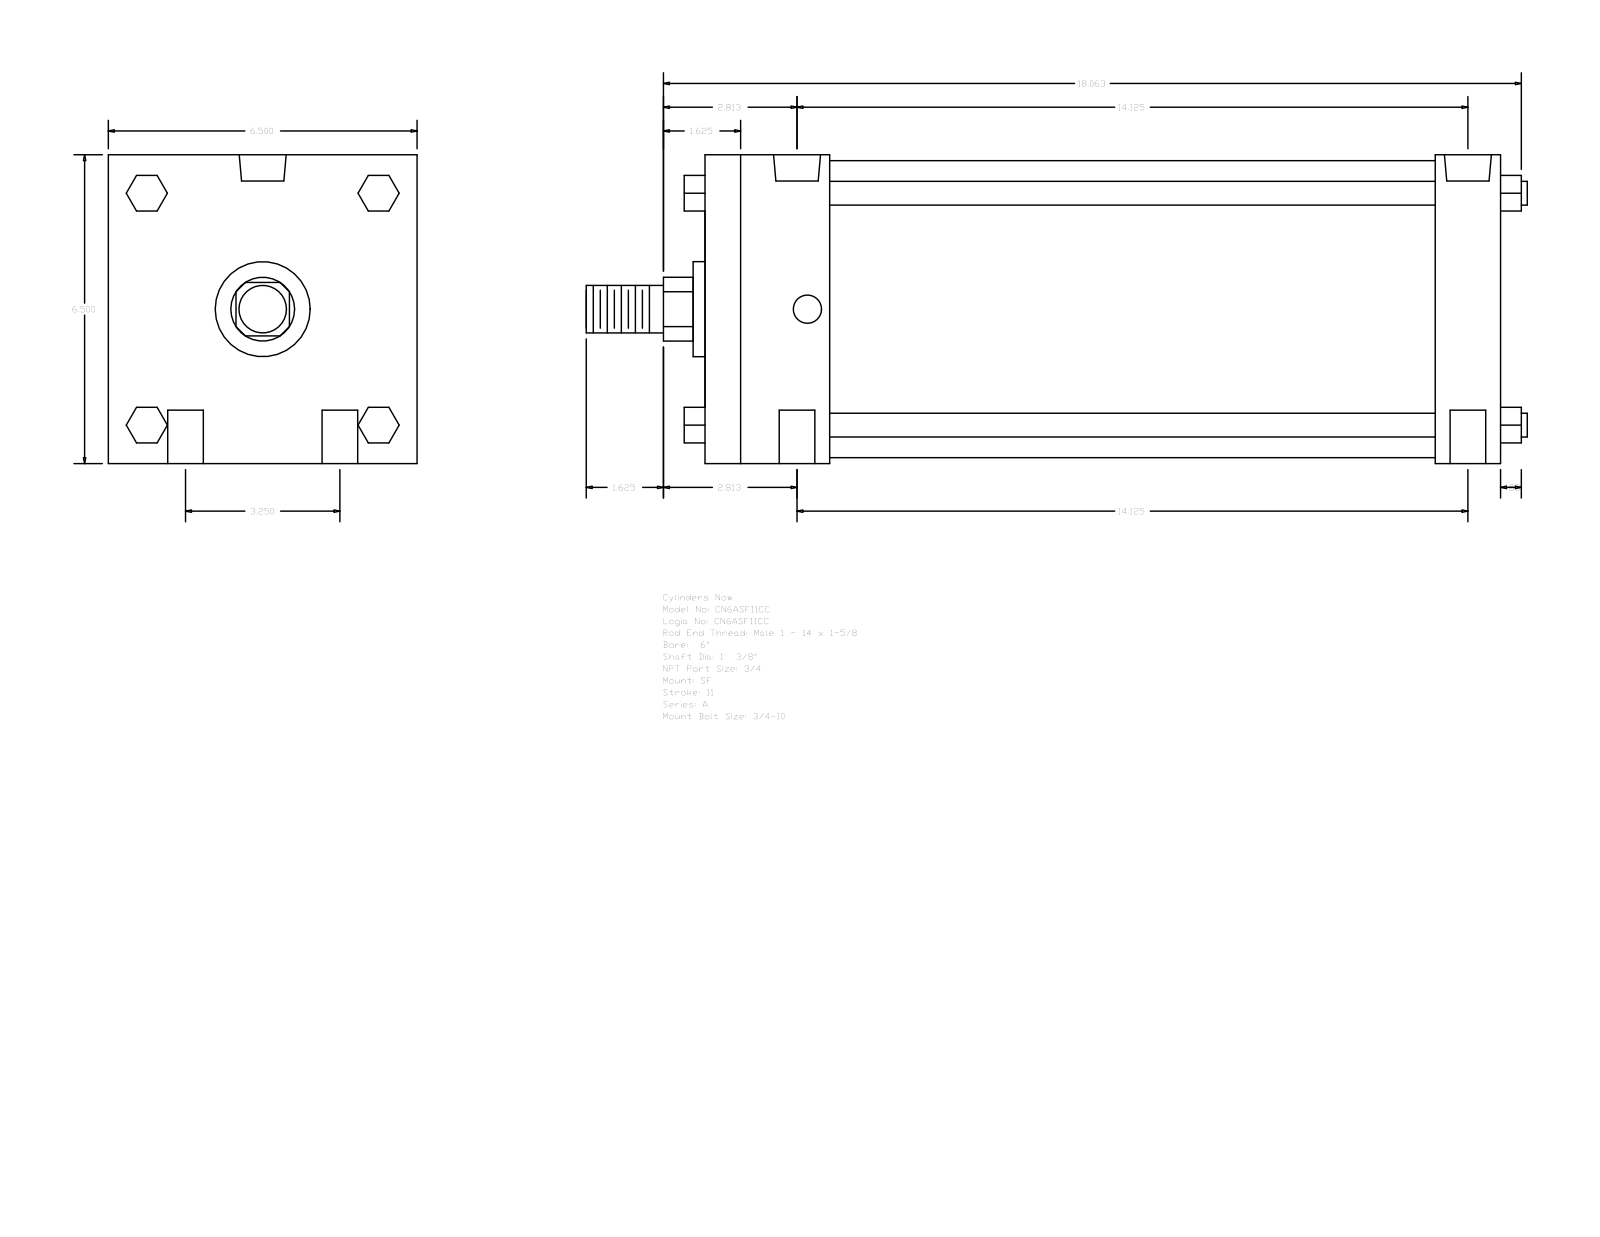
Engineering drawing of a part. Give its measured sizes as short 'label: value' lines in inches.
name: A_SF__0600_1.375
written by: GSSL Pune (CONFIG_CONTROL_DESIGN)
unit: in
bodies: 0 solids, 124 faces (94 planar, 30 cylindrical, 0 other)
size: 19.813 × 6.5 × 6.5
holes: 4× ⌀0.75, 2× ⌀0.594, 2× ⌀0.989
bosses: 4× ⌀0.5, 1× ⌀6.25, 1× ⌀2, 1× ⌀1.375, 1× ⌀1
rounds: 1× R0.672
face distances: 6.5, 16.75, 15.375, 1.375, 2.625, 12.75, 14.125, 0.75, 2.44, 4.226
hole spacings: 1.625, 14.218, 14.125, 3.25, 14.494, 13.687
